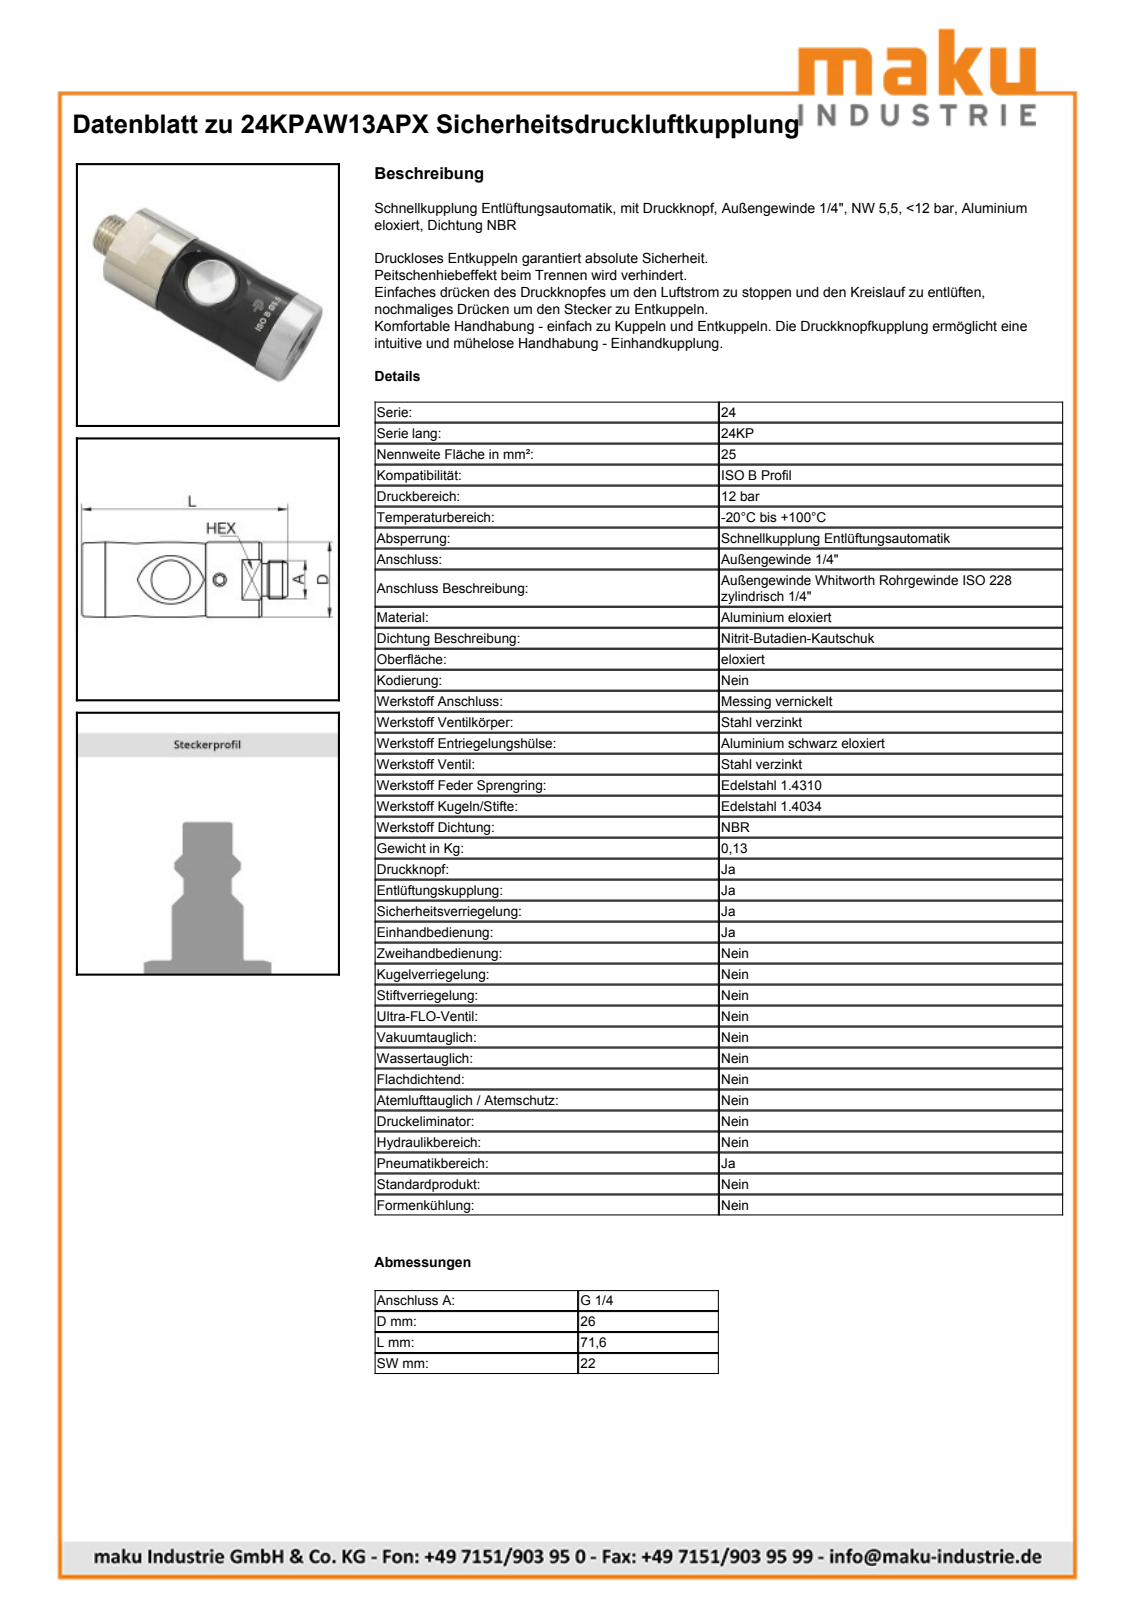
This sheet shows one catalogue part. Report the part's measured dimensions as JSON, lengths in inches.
{"part_name": "24KPAW13APX", "step_written_by": "Autodesk Inventor 2019 (CONFIG_CONTROL_DESIGN)", "units": "inches", "bodies": {"solids": 39, "faces": 225, "planar": 63, "cylindrical": 72, "other": 90}, "overall_size": [2.819, 1.024, 1.024], "volume_in3": 2.346, "surface_area_in2": 36.89, "round_holes": [[0.488, 2], [0.138, 1], [0.256, 1], [0.354, 1], [0.378, 1], [0.38, 1], [0.417, 1], [0.472, 1], [0.482, 1], [0.535, 1], [0.591, 1], [0.626, 1]], "round_bosses_or_shafts": [[1.024, 1], [0.889, 1], [0.866, 1], [0.807, 1], [0.713, 1], [0.65, 1], [0.639, 1], [0.622, 1]], "partial_cylinders_radius": [[0.244, 2]], "face_to_face_distances": [1.697, 1.378, 0.319, 0.768, 2.146, 2.465, 0.039, 2.425, 1.657, 0.28], "hole_center_spacings": [0.024, 0.028, 0.051, 0.671]}
